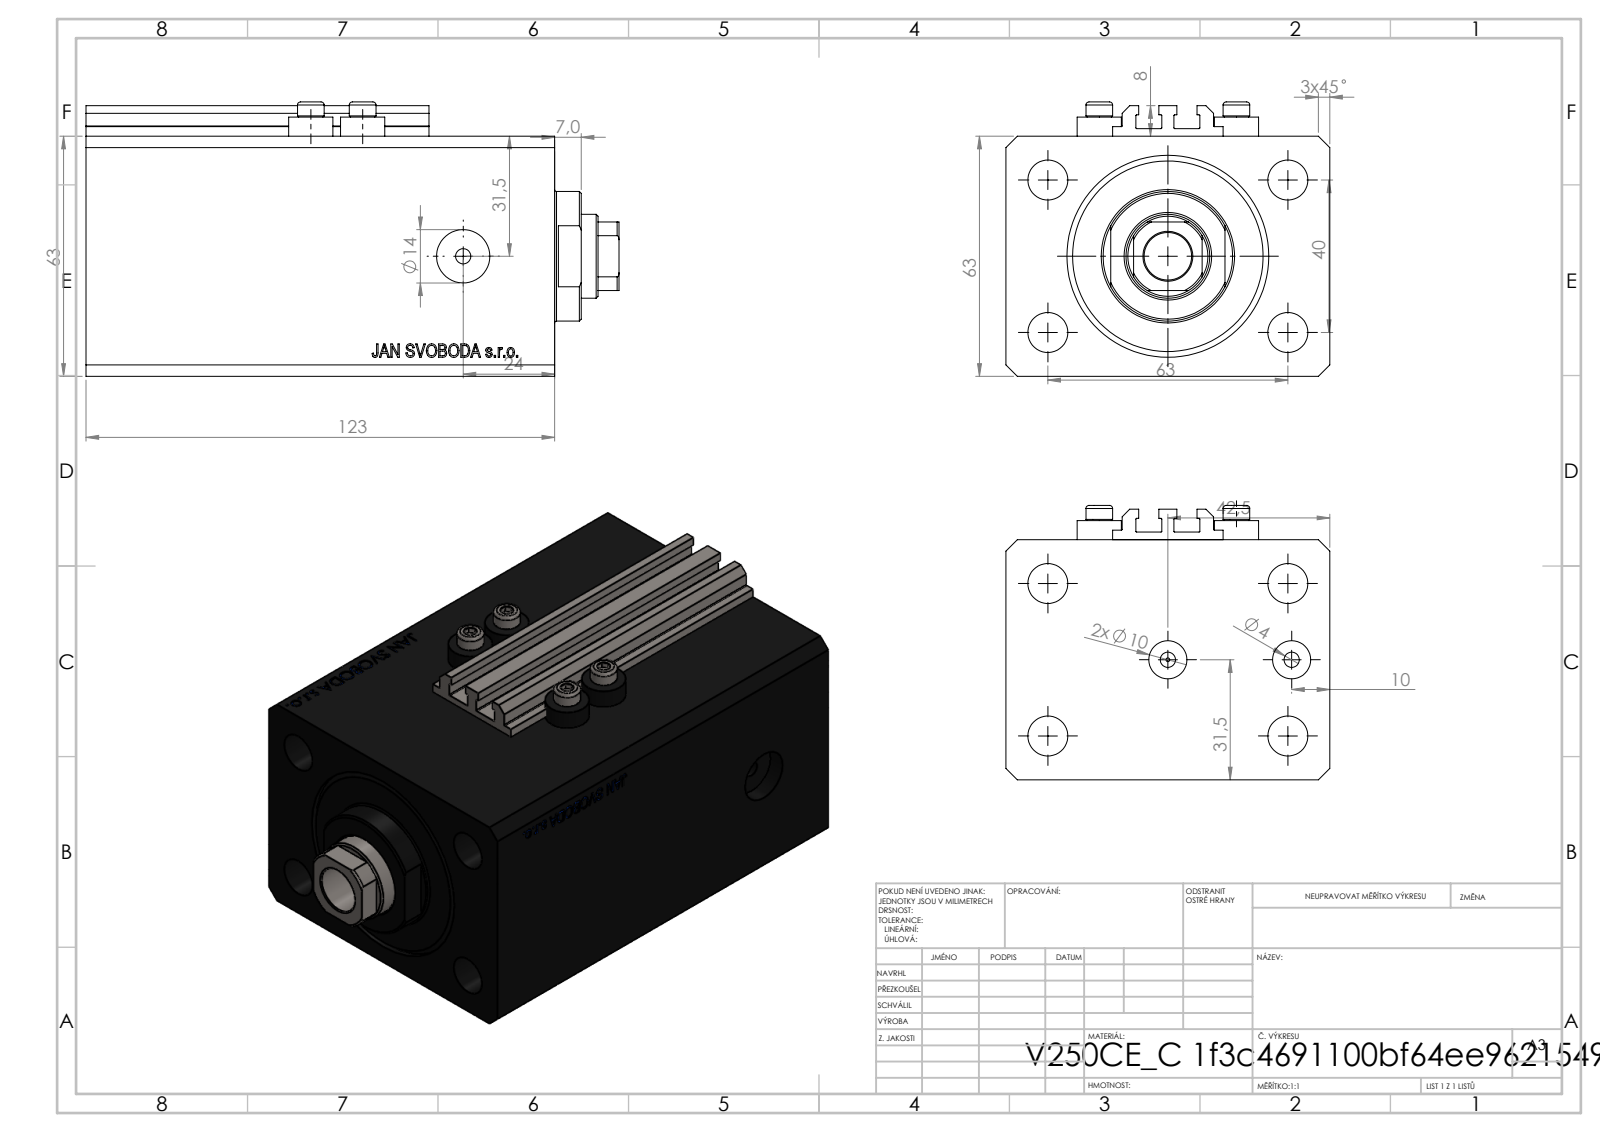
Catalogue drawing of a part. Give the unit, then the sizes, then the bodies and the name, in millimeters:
Units: millimetres
Overall size (bounding box): 140 × 85 × 72
Round holes (diameter × count): ⌀4 ×8, ⌀10.5 ×4, ⌀10 ×2, ⌀14 ×2, ⌀1.25 ×1, ⌀12.5 ×1, ⌀22 ×1, ⌀40 ×1, ⌀53 ×1
Round bosses / shafts (diameter × count): ⌀11.6 ×4, ⌀7 ×4, ⌀34 ×1
Partial cylindrical surfaces — rounded edges, fillets, slot ends (radius × count): R0.2 ×10, R10.5 ×1
Main face-to-face distances: 63, 85, 123, 17, 106, 11.4, 94.6, 111.6, 2.5, 10
Hole centre spacings: 37.31, 13.6, 20.02, 36, 38.48, 40, 63, 67.05
Volume: 586 857 mm³ · Surface area: 114 184 mm²
Bodies: 8 solids, 1038 faces (504 planar, 88 cylindrical, 446 other)
Part name (STEP PRODUCT): V250CE_C_Body; V250CE_VC_C; ALLEN BOLT V250CE; V250CE_C_VCP
STEP written by: SolidWorks 2019 (CONFIG_CONTROL_DESIGN)
